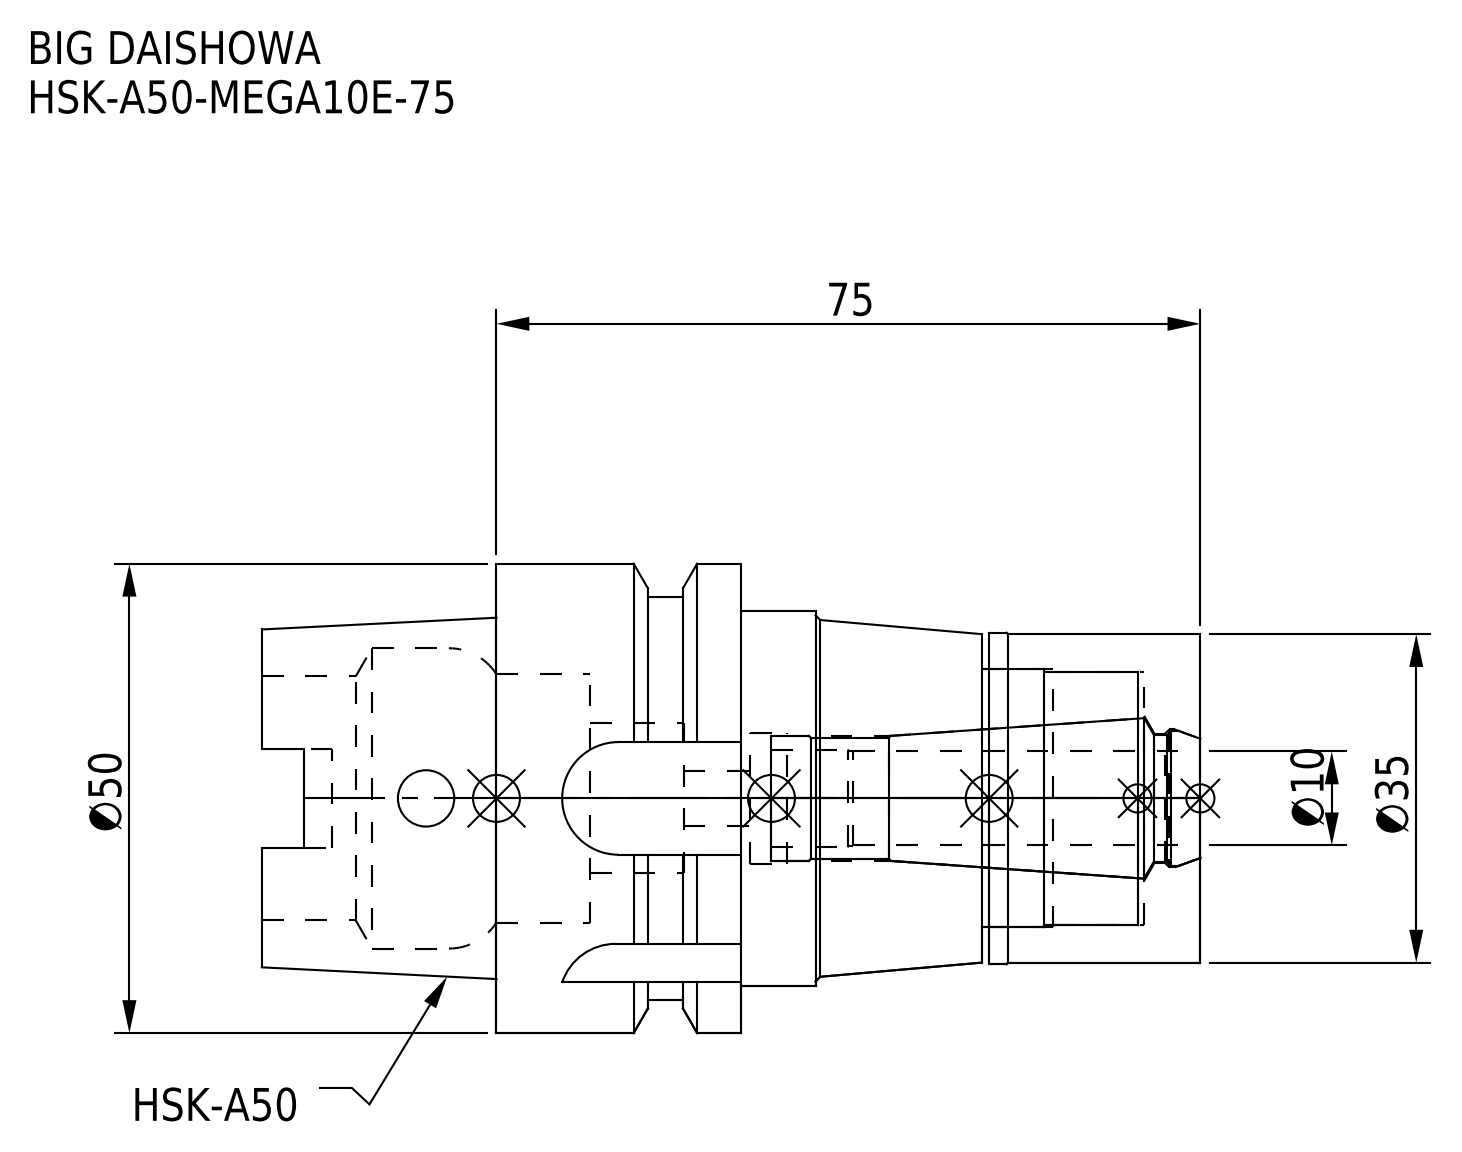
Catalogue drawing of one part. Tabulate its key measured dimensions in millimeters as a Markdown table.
| quantity | value |
| --- | --- |
| part name | HSK-A50-MEGA10E-75-100-FreeParts; HSK-A50-MEGA10E-75; HSK-A50-MEGA10E-75_1.stp; DXF_TEMP_ASSY_ASM_4_ASM.stp (+3 more) |
| STEP written by | SolidWorks 2019 (CONFIG_CONTROL_DESIGN) |
| units | millimeters |
| bodies | 2 solids, 126 faces (45 planar, 53 cylindrical, 28 other) |
| overall size | 100 × 50 × 50 |
| volume | 91 553 mm³ |
| surface area | 27 046 mm² |
| round holes (diameter × count) | 5.8 × 1, 6 × 1, 13.3 × 1, 13.8 × 1, 13.9 × 1, 14.7 × 1, 16 × 1, 26 × 1, 26.6 × 1, 27 × 1, 27.5 × 1, 32 × 1 |
| round bosses / shafts (diameter × count) | 50 × 1, 43 × 1, 40 × 1, 35.3 × 1, 35 × 1 |
| partial cylindrical surfaces (radius × count) | 2.38 × 4, 6 × 4 |
| main face-to-face distances | 75, 49, 26, 22.5, 26.5, 52.5, 23.3, 0.8, 25.7, 51.7 |
